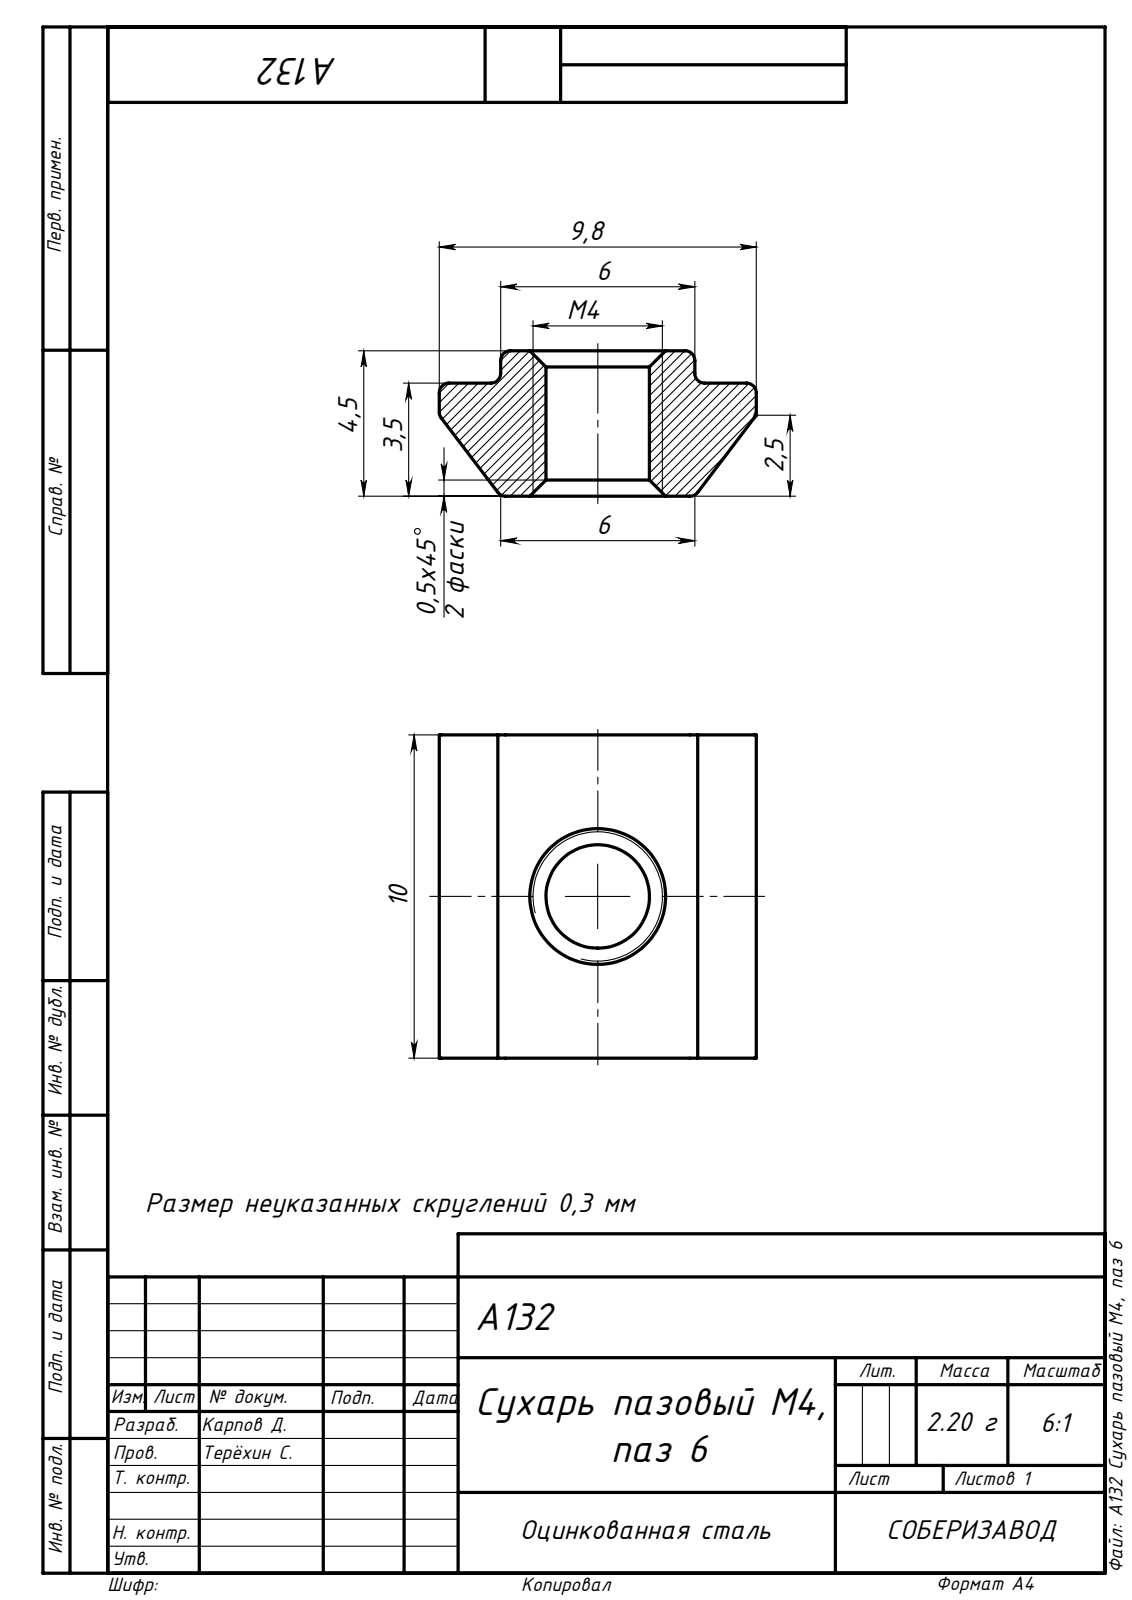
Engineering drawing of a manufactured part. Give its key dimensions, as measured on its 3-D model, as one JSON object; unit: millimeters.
{"part_name": "A132 Сухарь пазовый М4, паз 6", "step_written_by": "SolidWorks 2019 (AUTOMOTIVE_DESIGN)", "units": "millimeters", "bodies": {"solids": 1, "faces": 28, "planar": 12, "cylindrical": 12, "other": 4}, "overall_size": [10, 9.8, 4.5], "volume_mm3": 316, "surface_area_mm2": 347, "round_holes": [[3.2, 1]], "partial_cylinders_radius": [[0.3, 10]], "face_to_face_distances": [4.5, 10, 1, 3.5, 1.9, 7.9, 9.8, 6]}
